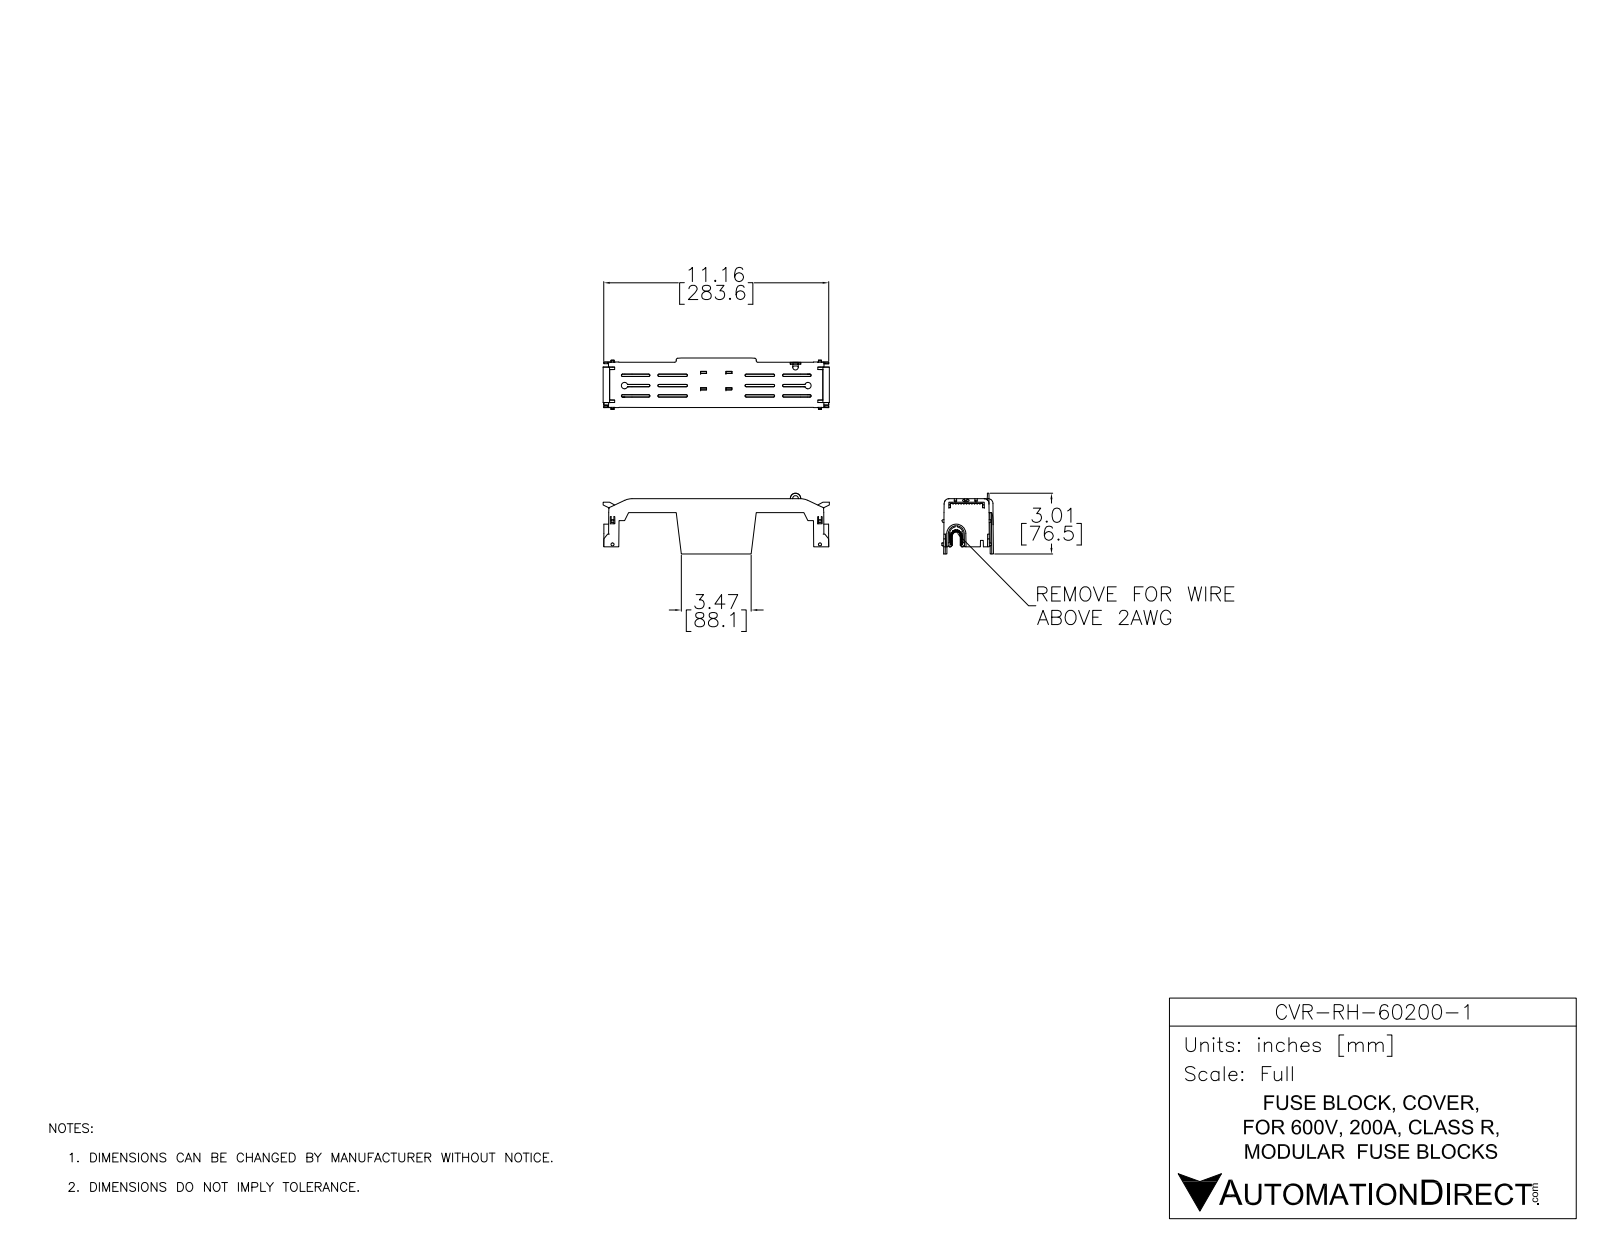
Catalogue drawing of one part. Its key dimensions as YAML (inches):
part_name: "CVR-RH-60200-1"
step_written_by: "SolidWorks 2017 (AUTOMOTIVE_DESIGN)"
units: inches
bodies: {solids: 1, faces: 1446, planar: 937, cylindrical: 106, other: 403}
overall_size: [11.215, 3.012, 2.553]
volume: 5.503
surface_area: 149.2
round_holes:
  - {diameter: 0.276, count: 1}
partial_cylinders:
  - {radius: 0.039, count: 16}
  - {radius: 0.118, count: 8}
  - {radius: 0.157, count: 7}
  - {radius: 0.236, count: 7}
  - {radius: 0.079, count: 6}
  - {radius: 0.01, count: 2}
  - {radius: 0.02, count: 2}
  - {radius: 0.197, count: 2}
face_to_face_distances: [0.079, 0.197, 0.118, 0.276, 0.512, 0.803, 0.624, 1.681, 1.76, 1.267]
